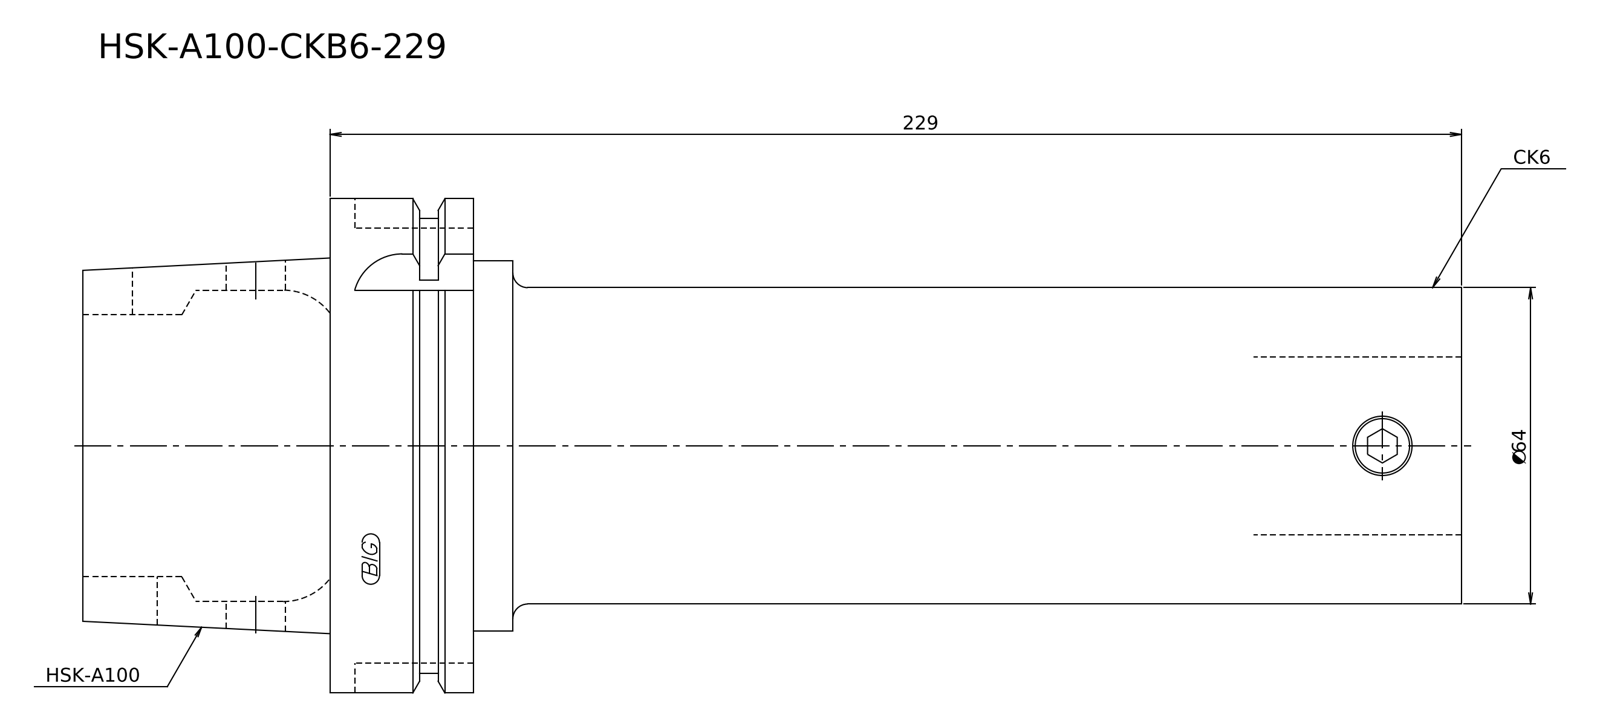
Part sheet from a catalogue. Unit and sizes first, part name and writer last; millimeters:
Units: millimetres
Overall size (bounding box): 279 × 100 × 100
Round bosses / shafts (diameter × count): ⌀100 ×1, ⌀92 ×1, ⌀75.8 ×1, ⌀75 ×1, ⌀64 ×1
Main face-to-face distances: 79, 29, 50, 200, 229, 279, 192, 8, 37, 87
Volume: 1 088 000 mm³ · Surface area: 77 653 mm²
Bodies: 1 solid, 17 faces (7 planar, 6 cylindrical, 4 other)
STEP written by: Kubotek KeyCreator V8.5.1 (14335) (CONFIG_CONTROL_DESIGN)
